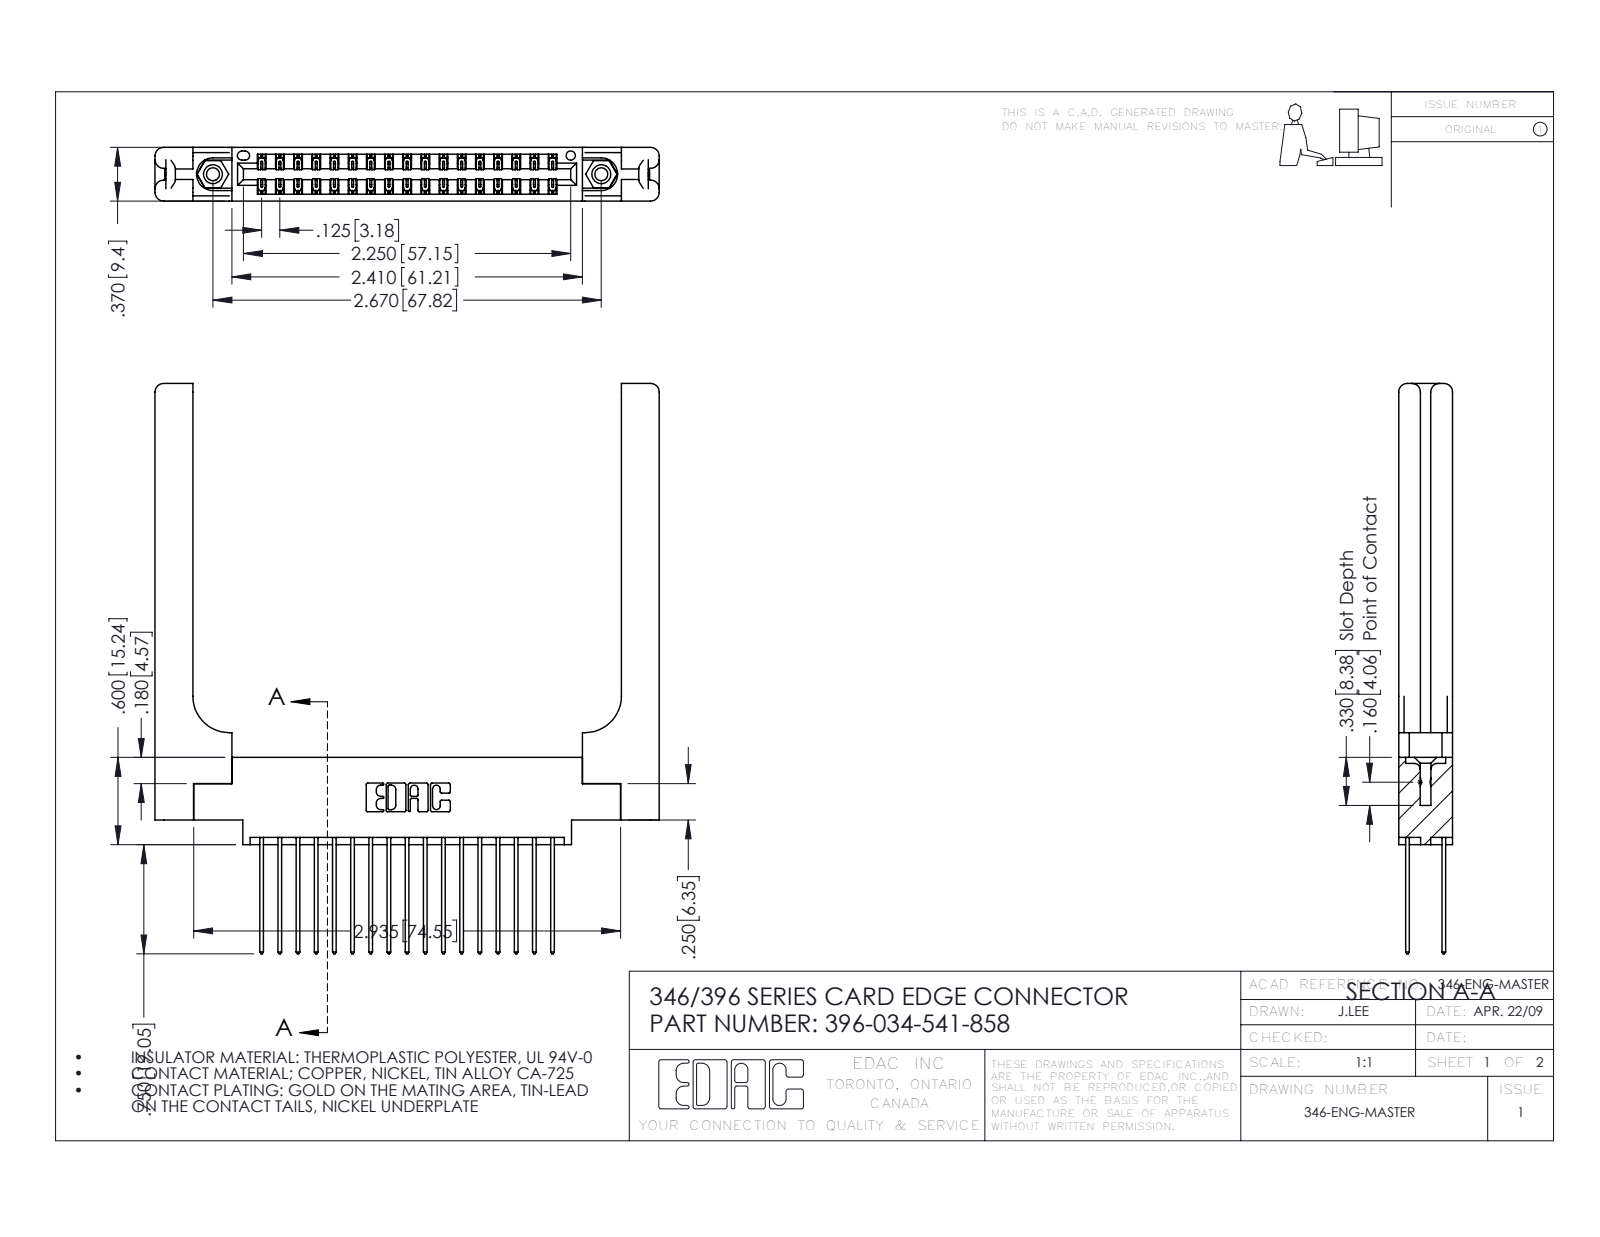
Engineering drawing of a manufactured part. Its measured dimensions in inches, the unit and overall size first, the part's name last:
Units: inches
Overall size (bounding box): 3.92 × 3.466 × 0.37
Round holes (diameter × count): ⌀0.089 ×2, ⌀0.125 ×2, ⌀0.156 ×2, ⌀0.064 ×1
Round bosses / shafts (diameter × count): ⌀0.155 ×2
Partial cylindrical surfaces — rounded edges, fillets, slot ends (radius × count): R0.006 ×51, R0.01 ×34, R0.01 ×22, R0.06 ×16, R0.007 ×6, R0.031 ×6, R0.026 ×3, R0.014 ×2
Main face-to-face distances: 0.37, 0.072, 0.048, 0.322, 0.25, 0.15, 0.148, 0.025, 0.298, 0.077
Hole centre spacings: 0.246, 2.463, 2.67
Volume: 0.972 in³ · Surface area: 26.79 in²
Bodies: 39 solids, 2150 faces (1418 planar, 672 cylindrical, 60 other)
Part name (STEP PRODUCT): 396-034-541-858; 345-292-001_345-293-141; 345-250-001_345-250-001-102; 346-220-058_345-220-058 (+1 more)
STEP written by: SolidWorks 2016 (CONFIG_CONTROL_DESIGN)
